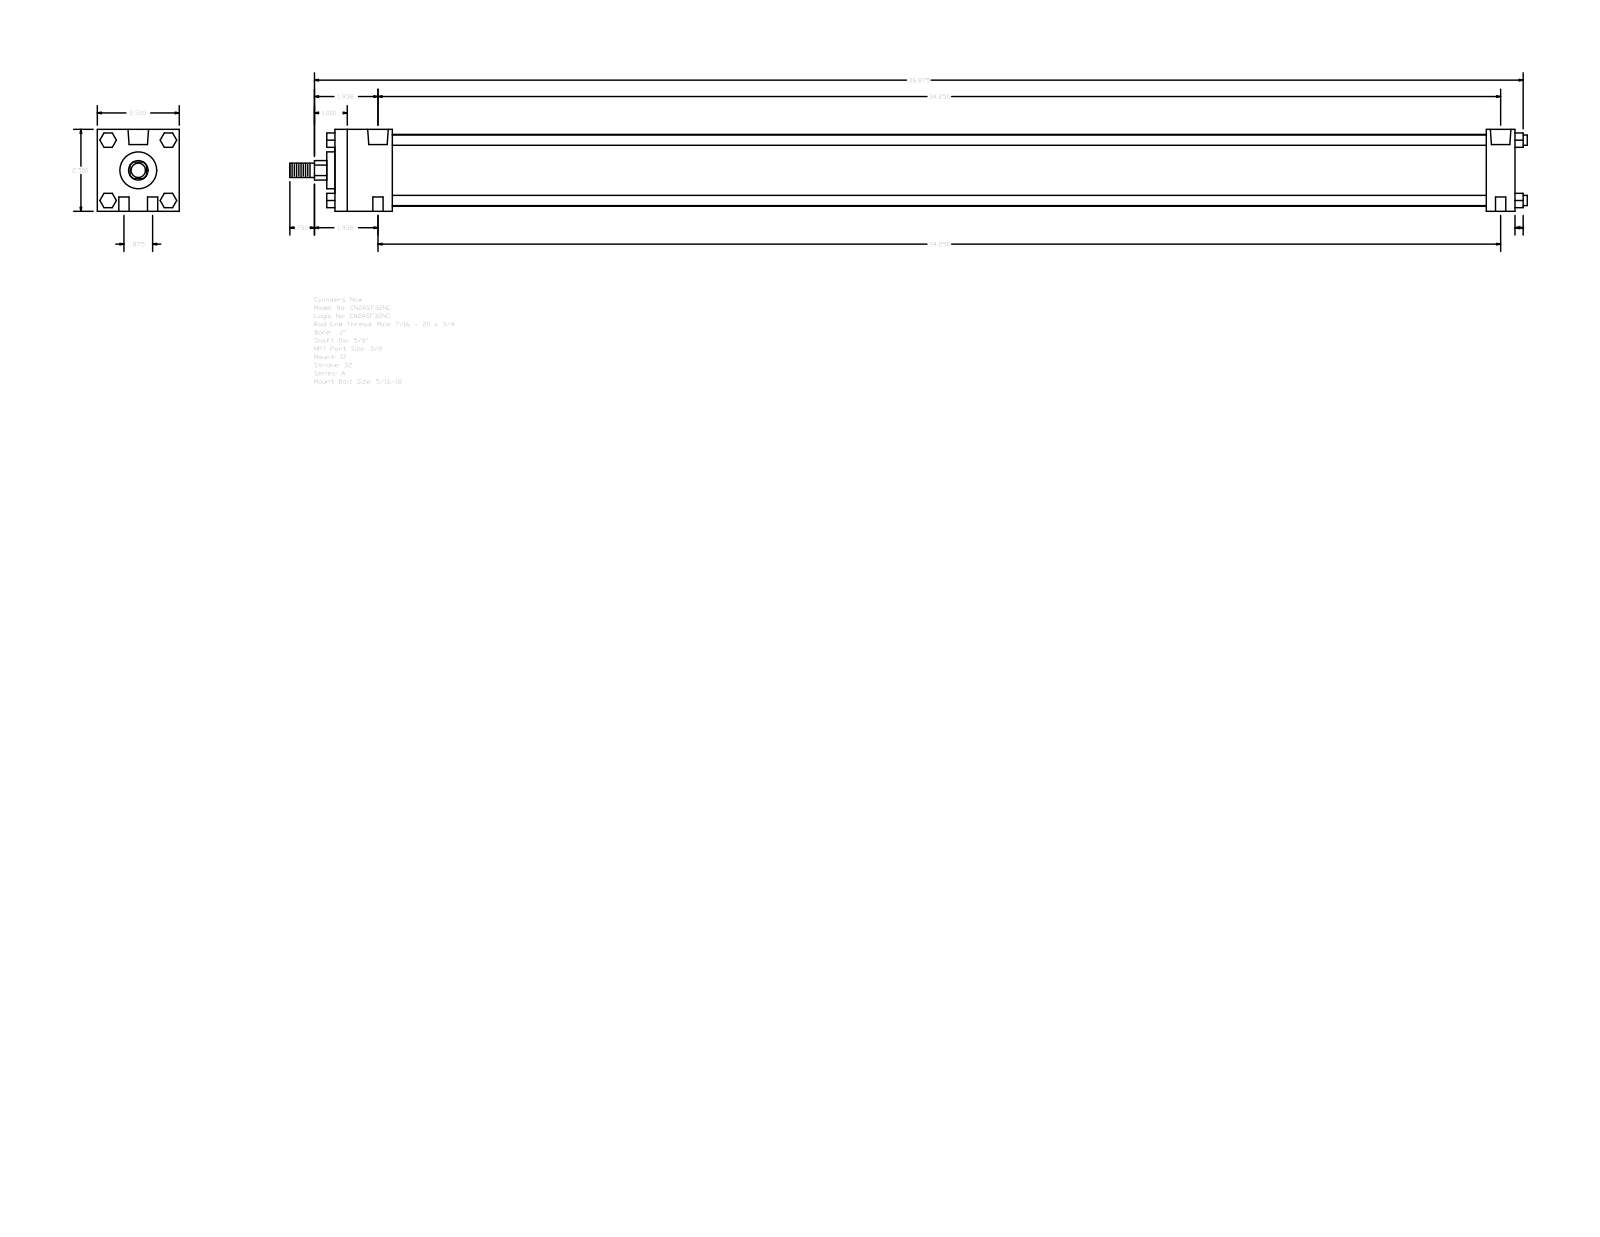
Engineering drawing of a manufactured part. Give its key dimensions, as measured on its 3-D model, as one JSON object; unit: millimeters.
{"part_name": "A_SF__0200_0.625", "step_written_by": "GSSL Pune (CONFIG_CONTROL_DESIGN)", "units": "millimeters", "bodies": {"solids": 0, "faces": 124, "planar": 94, "cylindrical": 30, "other": 0}, "overall_size": [958.85, 63.5, 63.5], "round_holes": [[7.94, 4], [5.56, 2], [15.93, 2]], "round_bosses_or_shafts": [[7.94, 4], [55.63, 1], [28.57, 1], [15.88, 1], [11.11, 1]], "partial_cylinders_radius": [[7.54, 1]], "face_to_face_distances": [63.5, 914.39, 892.17, 22.22, 44.45, 847.72, 869.94, 6.35, 920.74, 50.8], "hole_center_spacings": [11.11, 870.02, 869.95, 22.22, 870.23, 862]}
